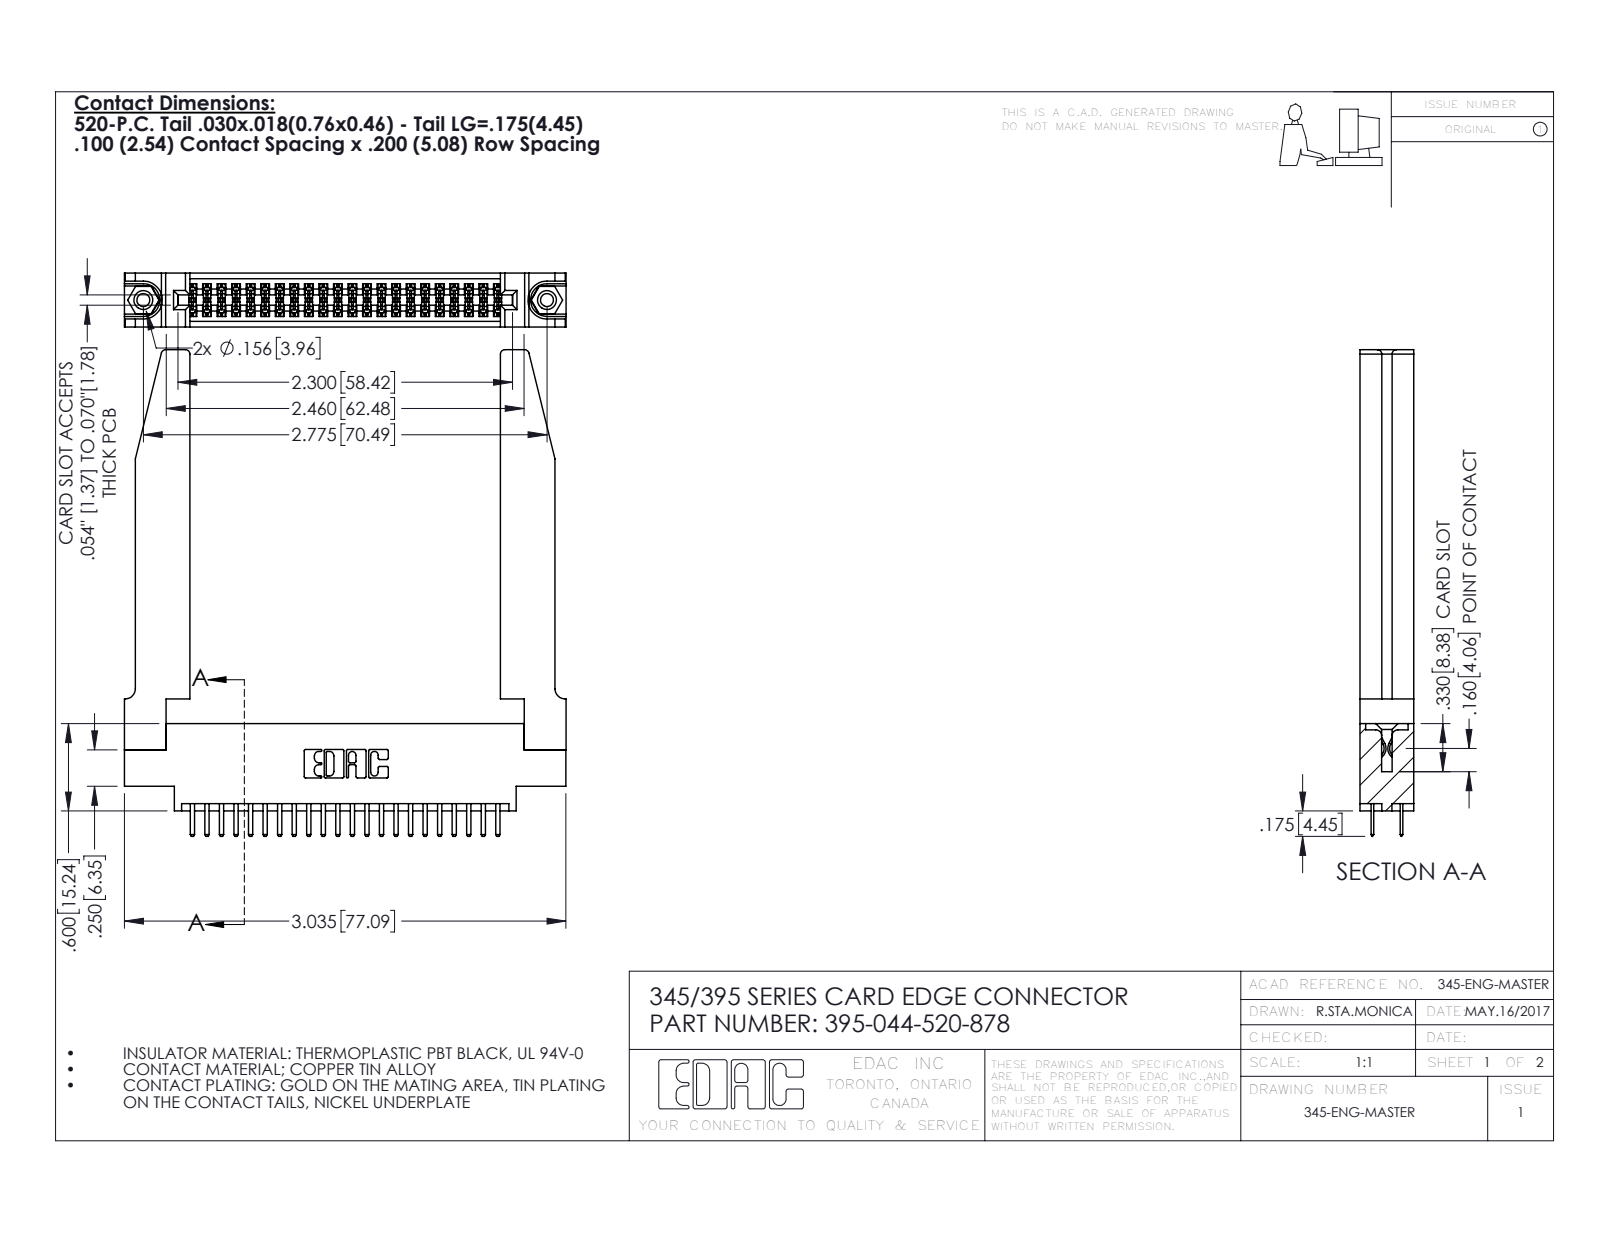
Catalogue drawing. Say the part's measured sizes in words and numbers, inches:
The part is named "395-044-520-878; 345-292-001_345-293-120; 345 Part_0.170 Offset - 0.156 Dia-TH; 345-220-078_345-220-078 (+1 more)". Its 3-D file was written by "SolidWorks 2016 (CONFIG_CONTROL_DESIGN)". It is 49 solids with 2740 faces: 1766 planar, 922 cylindrical and 52 other. Overall it measures 3.345 by 3.036 by 0.37 inches. Its volume is 0.912 cubic inches and its surface area 26.59 square inches. Round holes: 2 of diameter 0.089, 2 of diameter 0.125, 2 of diameter 0.156, 1 of diameter 0.064. Round bosses or shafts: 2 of diameter 0.155. Partial cylindrical surfaces (rounded edges, fillets, slot ends): 66 of radius 0.006, 48 of radius 0.01, 22 of radius 0.01, 8 of radius 0.03, 6 of radius 0.007, 6 of radius 0.031, 3 of radius 0.026, 2 of radius 0.014. The main face-to-face distances are 0.37, 0.072, 0.298, 0.2, 0.098, 0.272, 0.025, 0.225, 0.123, 0.15. The hole center spacings are 0.27, 2.541, 2.775.
